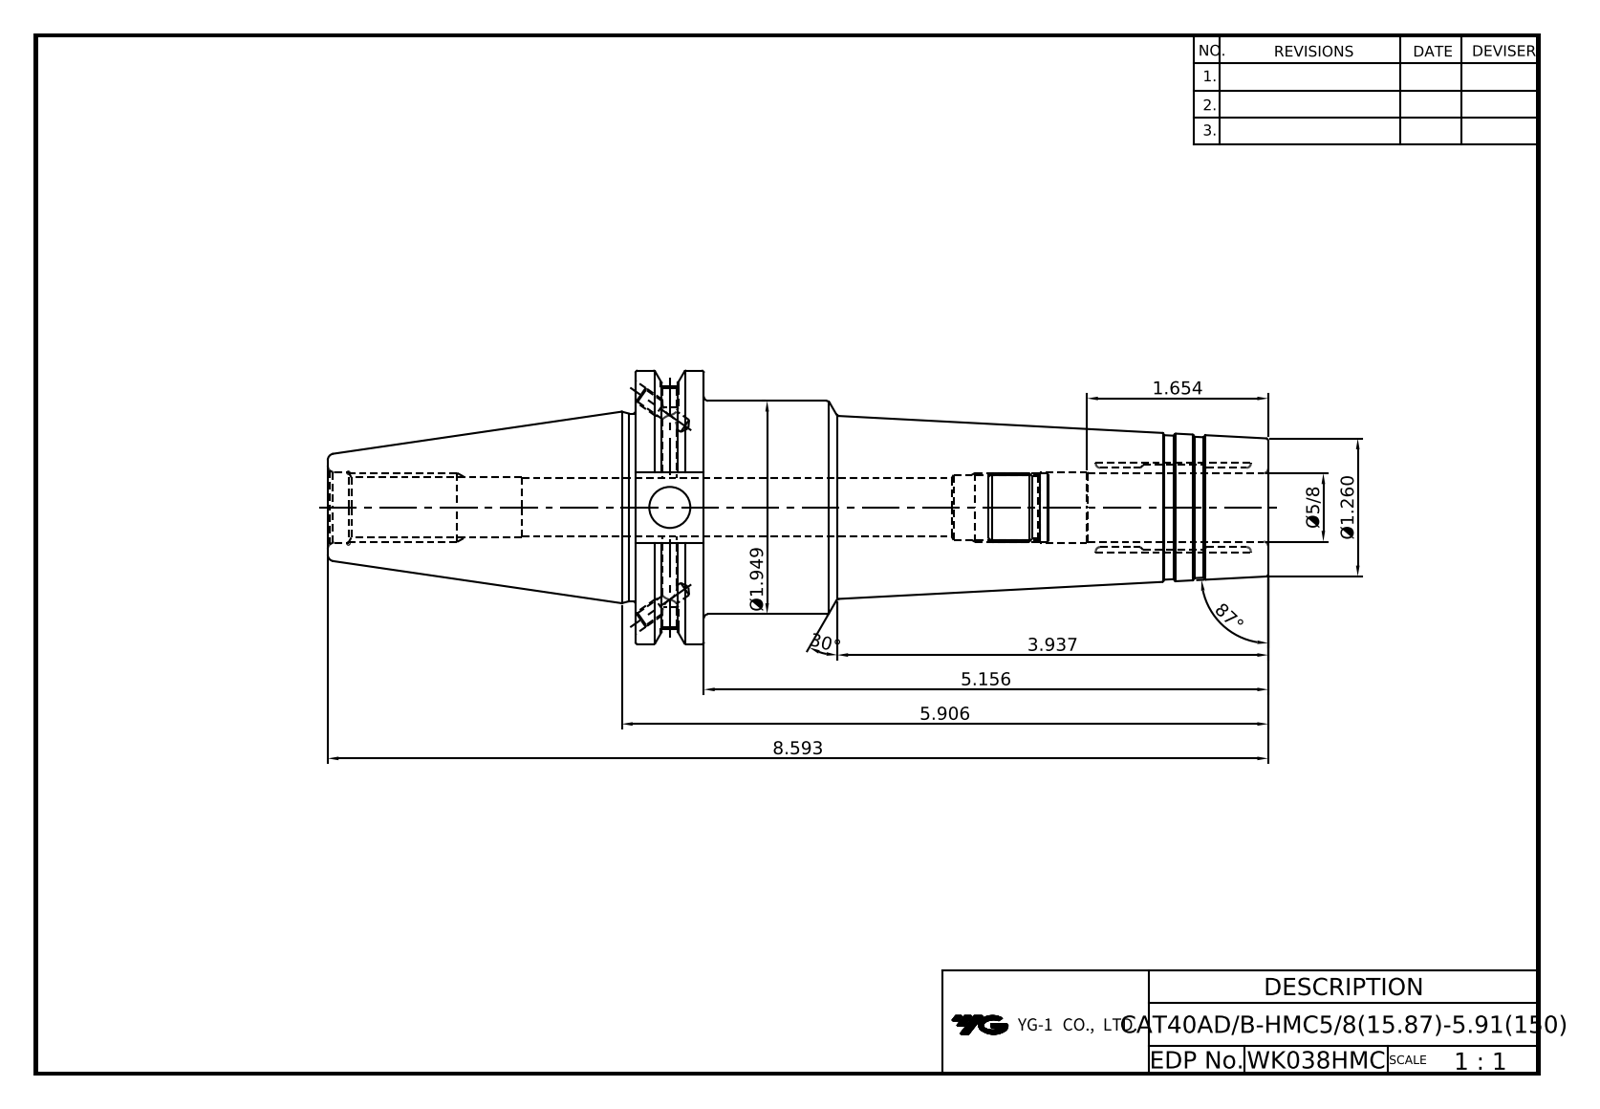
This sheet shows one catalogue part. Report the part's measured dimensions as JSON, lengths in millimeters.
{"part_name": "LO-CAT40ADB-HMC15.875-150", "step_written_by": "Autodesk Inventor 2020 (AUTOMOTIVE_DESIGN)", "units": "millimeters", "bodies": {"solids": 1, "faces": 106, "planar": 36, "cylindrical": 30, "other": 40}, "overall_size": [218.25, 63.5, 61.09], "volume_mm3": 248620, "surface_area_mm2": 42153, "round_holes": [[3.24, 4], [4, 2], [4.2, 2], [9.53, 1], [10.92, 1], [13, 1], [13.39, 1], [15.88, 1], [16.3, 1], [16.4, 1]], "round_bosses_or_shafts": [[63.5, 1], [49.5, 1], [43.6, 1]], "partial_cylinders_radius": [[8.19, 1], [28.15, 1]], "face_to_face_distances": [15.88, 146.83, 130.95, 47.6, 16.38, 71.42, 87.3, 218.25, 167.25, 95.83]}
